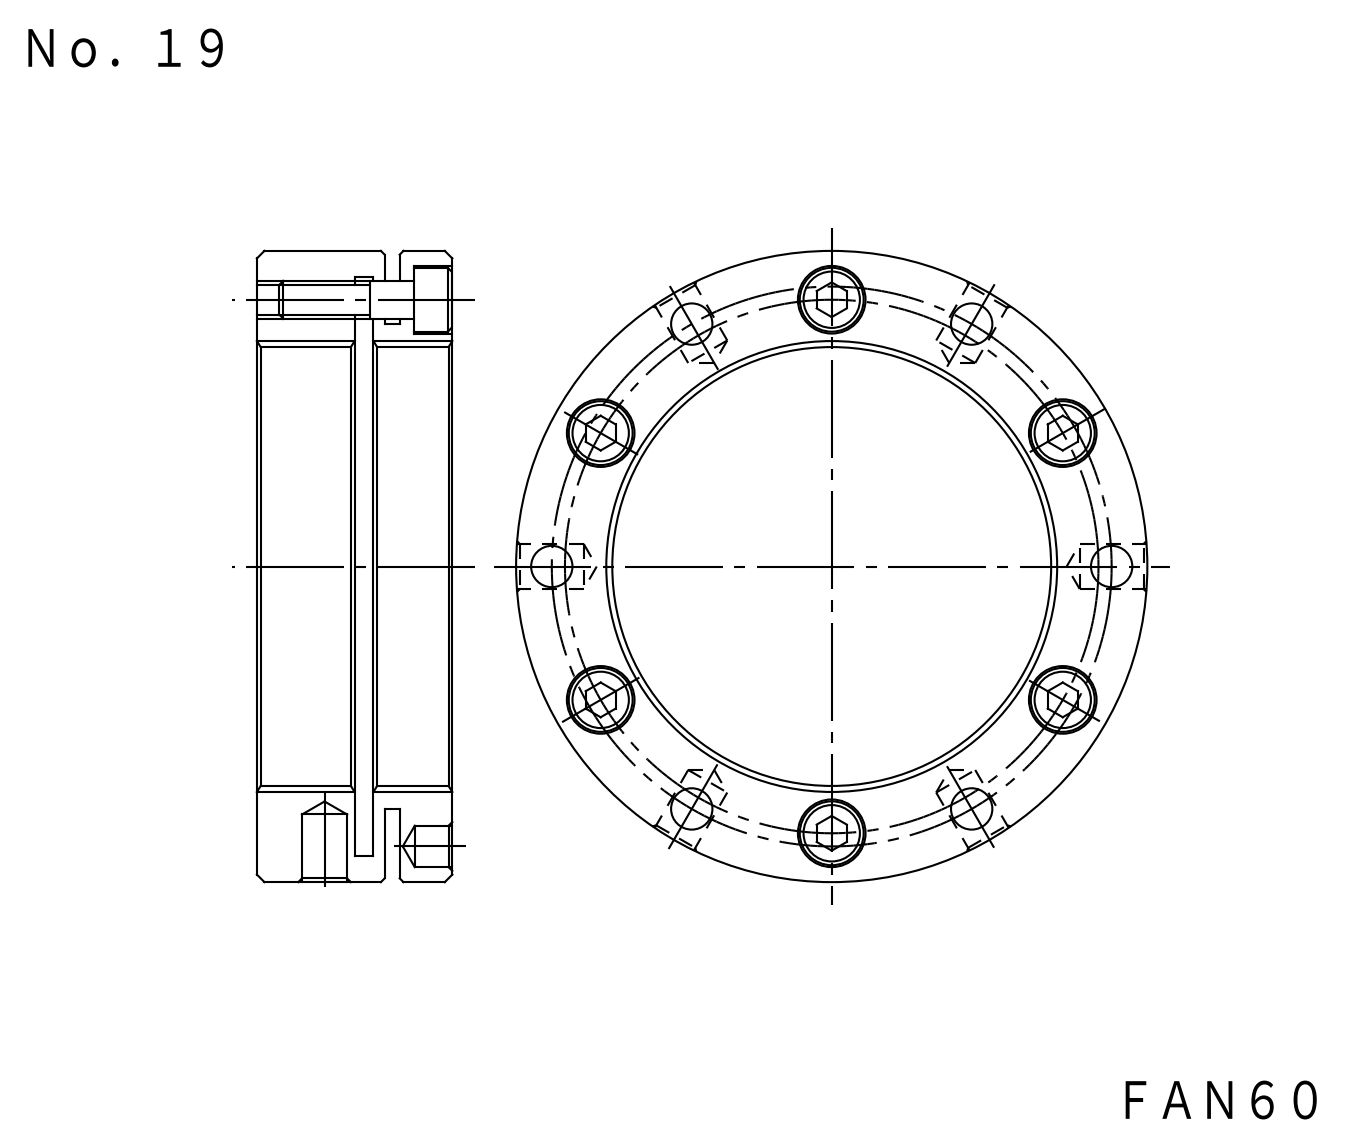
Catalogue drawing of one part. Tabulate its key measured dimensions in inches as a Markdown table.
| quantity | value |
| --- | --- |
| part name | FKD FAN60; M5X18_default |
| STEP written by | SolidWorks 2012 (CONFIG_CONTROL_DESIGN) |
| units | inches |
| bodies | 7 solids, 204 faces (72 planar, 108 cylindrical, 24 other) |
| overall size | 3.307 × 3.307 × 1.024 |
| volume | 3.572 in³ |
| surface area | 48.86 in² |
| round holes (diameter × count) | 0.163 × 6, 0.209 × 6, 0.217 × 6, 0.354 × 6, 0.236 × 3, 2.362 × 1, 3.071 × 1 |
| round bosses / shafts (diameter × count) | 0.335 × 6, 0.197 × 6, 3.307 × 1, 2.598 × 1 |
| main face-to-face distances | 0.098, 0.157, 1.024, 0.642, 0.382, 0.74, 0.283, 0.484, 0.256, 0.539 |
| hole center spacings | 1.417, 0.748, 1.467, 2.786, 2.039, 2.455, 2.54, 2.04 |
